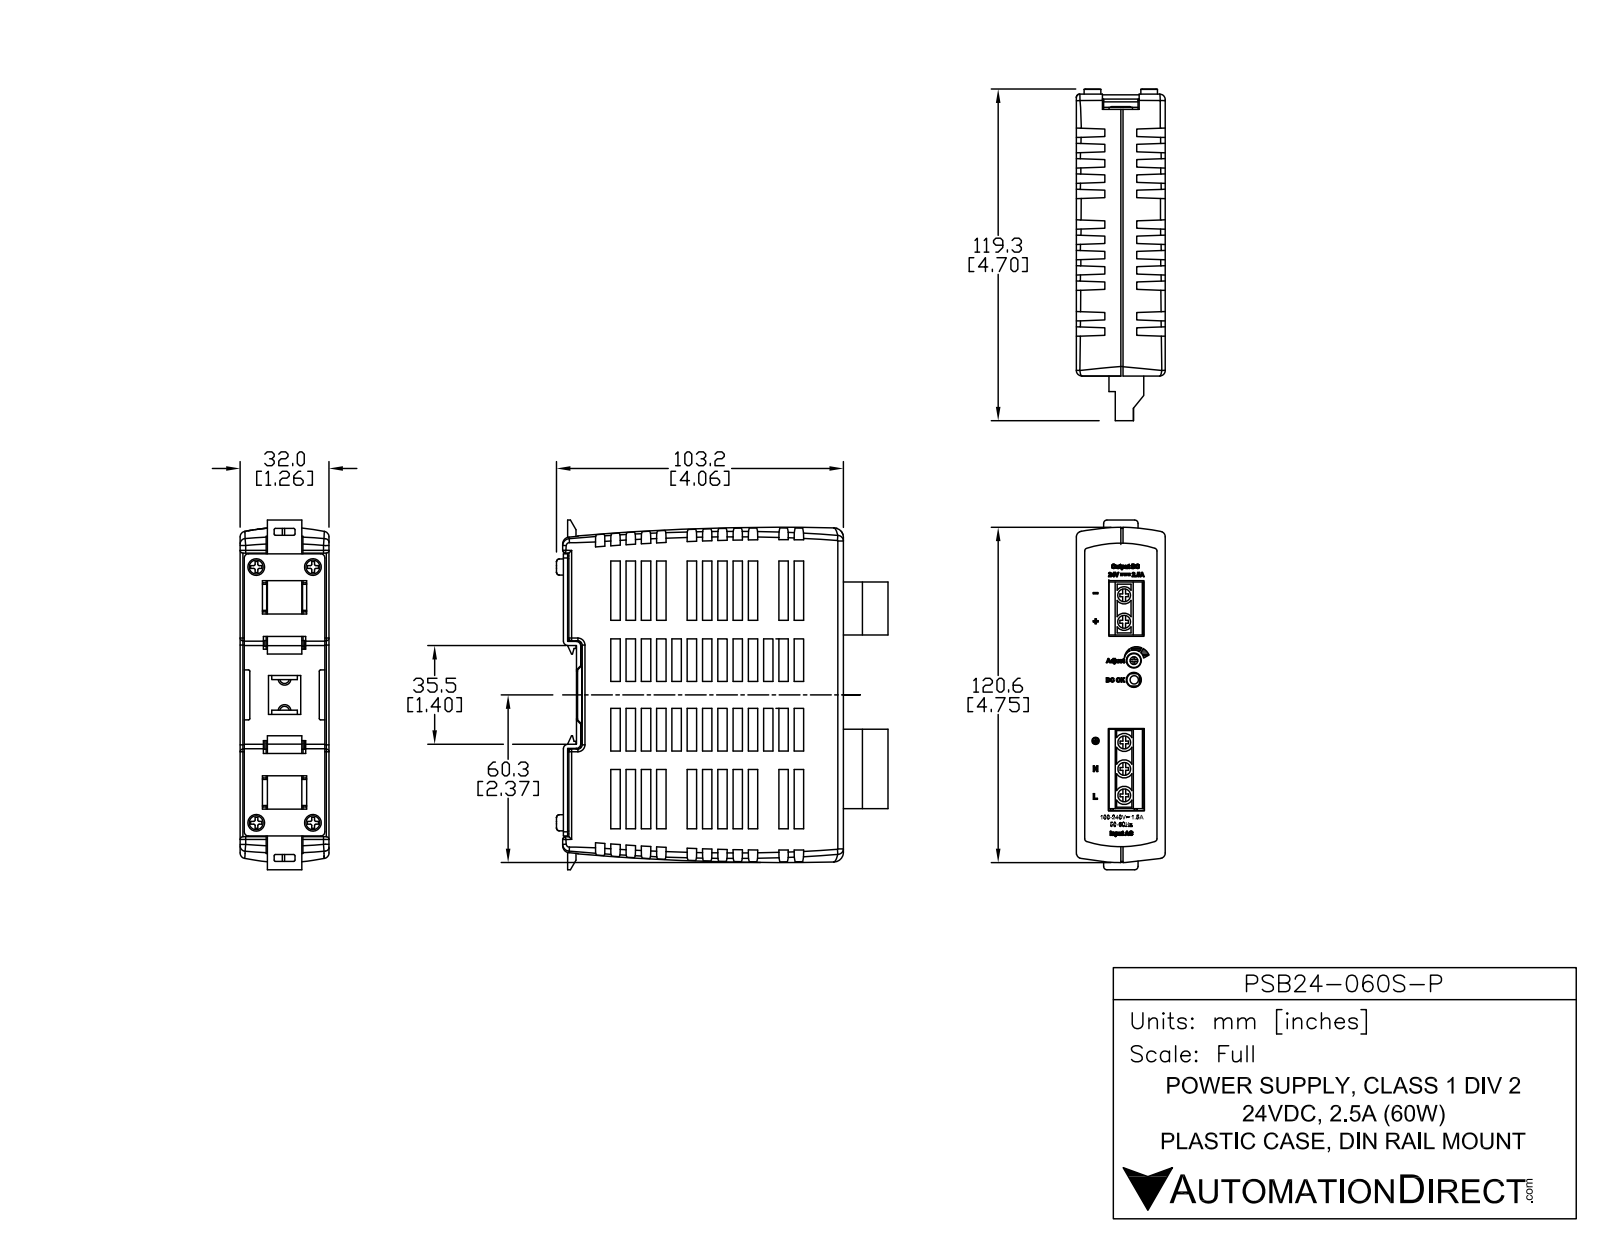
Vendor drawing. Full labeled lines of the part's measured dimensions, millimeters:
Part name (STEP PRODUCT): ASSY_LACH_ASM; 3268332100; 331406480000; 3109011900 (+8 more)
STEP written by: SolidWorks 2014 (AUTOMOTIVE_DESIGN)
Units: millimetres
Bodies: 26 solids, 4272 faces (2280 planar, 1055 cylindrical, 937 other)
Overall size (bounding box): 125.8 × 119.03 × 32
Volume: 103 000 mm³ · Surface area: 135 847 mm²
Round holes (diameter × count): ⌀1 ×8, ⌀3.5 ×6, ⌀1.95 ×5, ⌀2.5 ×5, ⌀4.6 ×5, ⌀4.9 ×5, ⌀1.1 ×4, ⌀4.4 ×4, ⌀0.56 ×3, ⌀0.8 ×2, ⌀4.2 ×2, ⌀4.5 ×2
Round bosses / shafts (diameter × count): ⌀3 ×6, ⌀5.2 ×5, ⌀0.46 ×3, ⌀4.67 ×2, ⌀0.95 ×2, ⌀0.6 ×2, ⌀8.8 ×1, ⌀6.8 ×1
Partial cylindrical surfaces — rounded edges, fillets, slot ends (radius × count): R0.5 ×176, R0.3 ×102, R0.9 ×20, R1 ×20, R2 ×11, R2.48 ×10, R1.5 ×7, R0.1 ×6
Main face-to-face distances: 1.6, 2.3, 29.7, 5.5, 3.5, 5.1, 2, 7.1, 23.9, 27.4
Hole centre spacings: 9.52, 0.85, 92, 9.56, 62.55, 62.56, 0.4, 3.59
